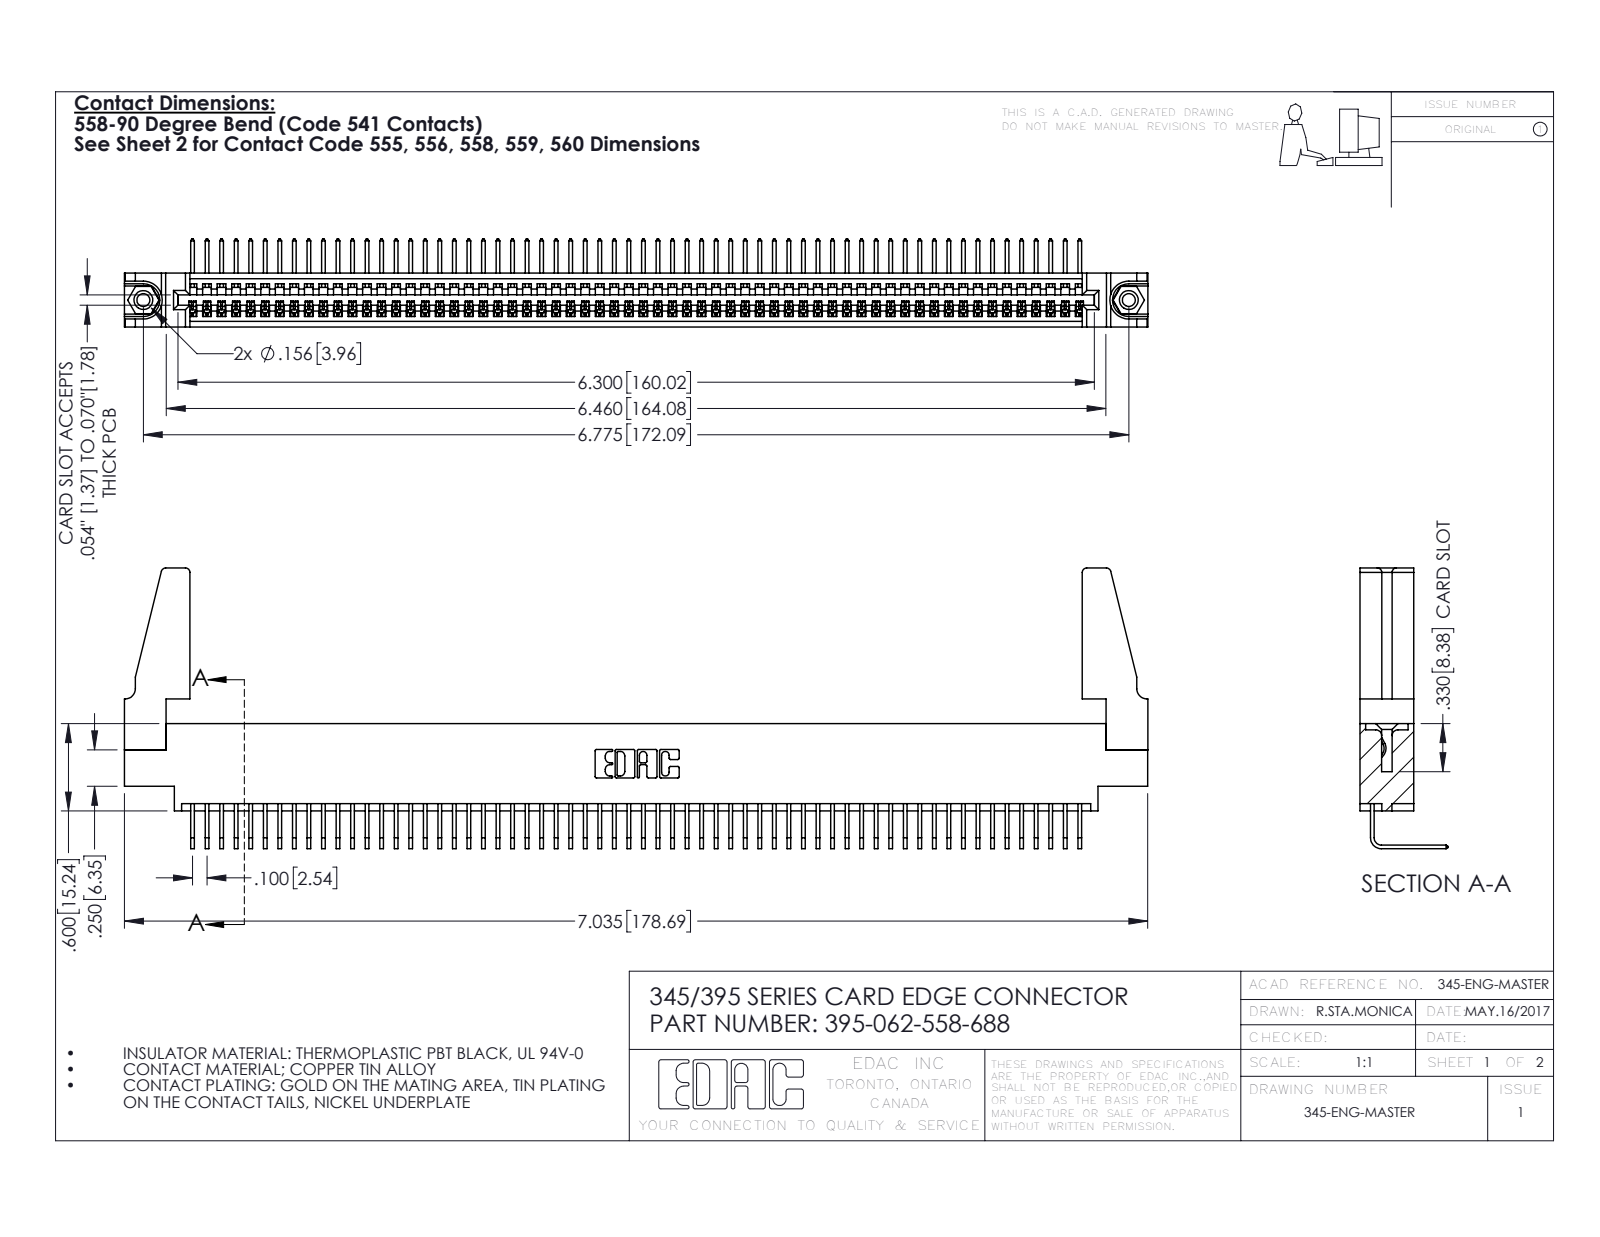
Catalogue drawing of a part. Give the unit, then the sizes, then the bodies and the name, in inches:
Units: inches
Overall size (bounding box): 7.036 × 1.929 × 0.605
Round holes (diameter × count): ⌀0.089 ×2, ⌀0.125 ×2, ⌀0.156 ×2, ⌀0.064 ×1
Round bosses / shafts (diameter × count): ⌀0.155 ×2
Partial cylindrical surfaces — rounded edges, fillets, slot ends (radius × count): R0.006 ×124, R0.01 ×22, R0.03 ×8, R0.007 ×6, R0.031 ×6, R0.026 ×3, R0.031 ×2, R0.04 ×2
Main face-to-face distances: 0.072, 0.298, 0.37, 0.098, 0.272, 0.025, 0.2, 0.225, 0.175, 0.149
Hole centre spacings: 0.27, 6.539, 6.775
Volume: 1.25 in³ · Surface area: 42.84 in²
Bodies: 67 solids, 3974 faces (2760 planar, 1198 cylindrical, 16 other)
Part name (STEP PRODUCT): 345-292-001_558 Tail - 2; 345-220-078_345-220-088; 395-062-558-688; 345-250-001_345-250-001-102 (+1 more)
STEP written by: SolidWorks 2016 (CONFIG_CONTROL_DESIGN)
